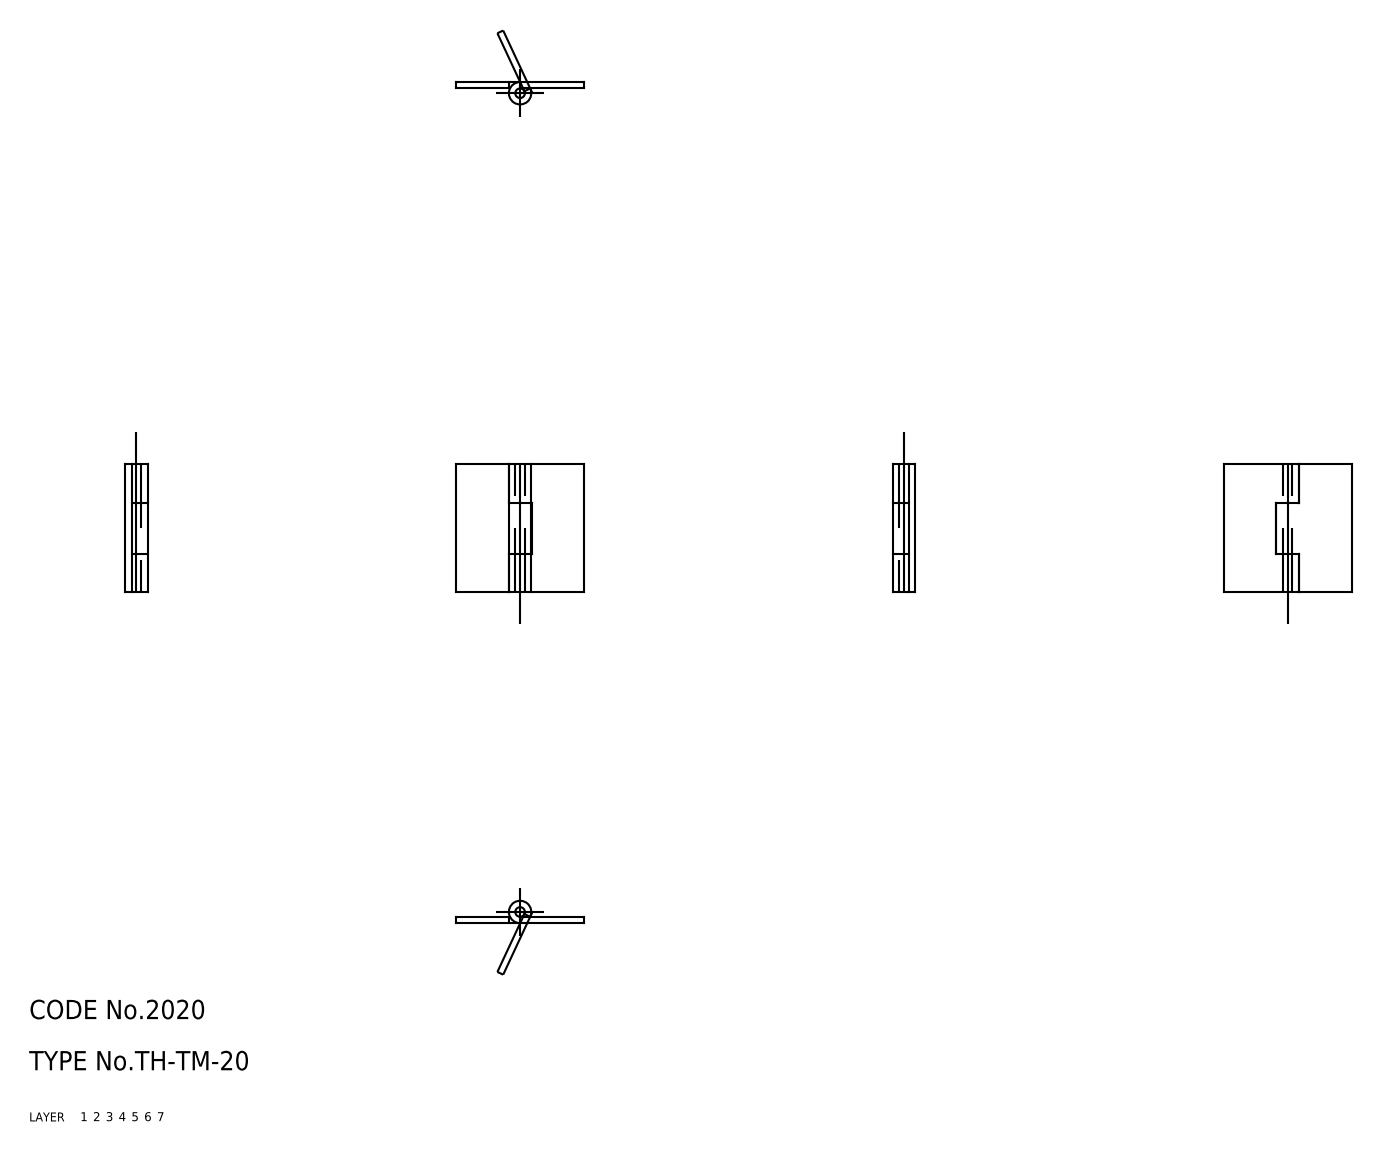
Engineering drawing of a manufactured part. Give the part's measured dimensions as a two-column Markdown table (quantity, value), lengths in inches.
| quantity | value |
| --- | --- |
| part name | hinge piece_B; hinge piece_A; shaft; TH_TM_20_21948_36 |
| STEP written by | CADfix (AUTOMOTIVE_DESIGN) |
| units | inches |
| bodies | 3 solids, 30 faces (0 planar, 0 cylindrical, 30 other) |
| overall size | 0.787 × 0.787 × 0.138 |
| volume | 0.032 in³ |
| surface area | 1.928 in² |
